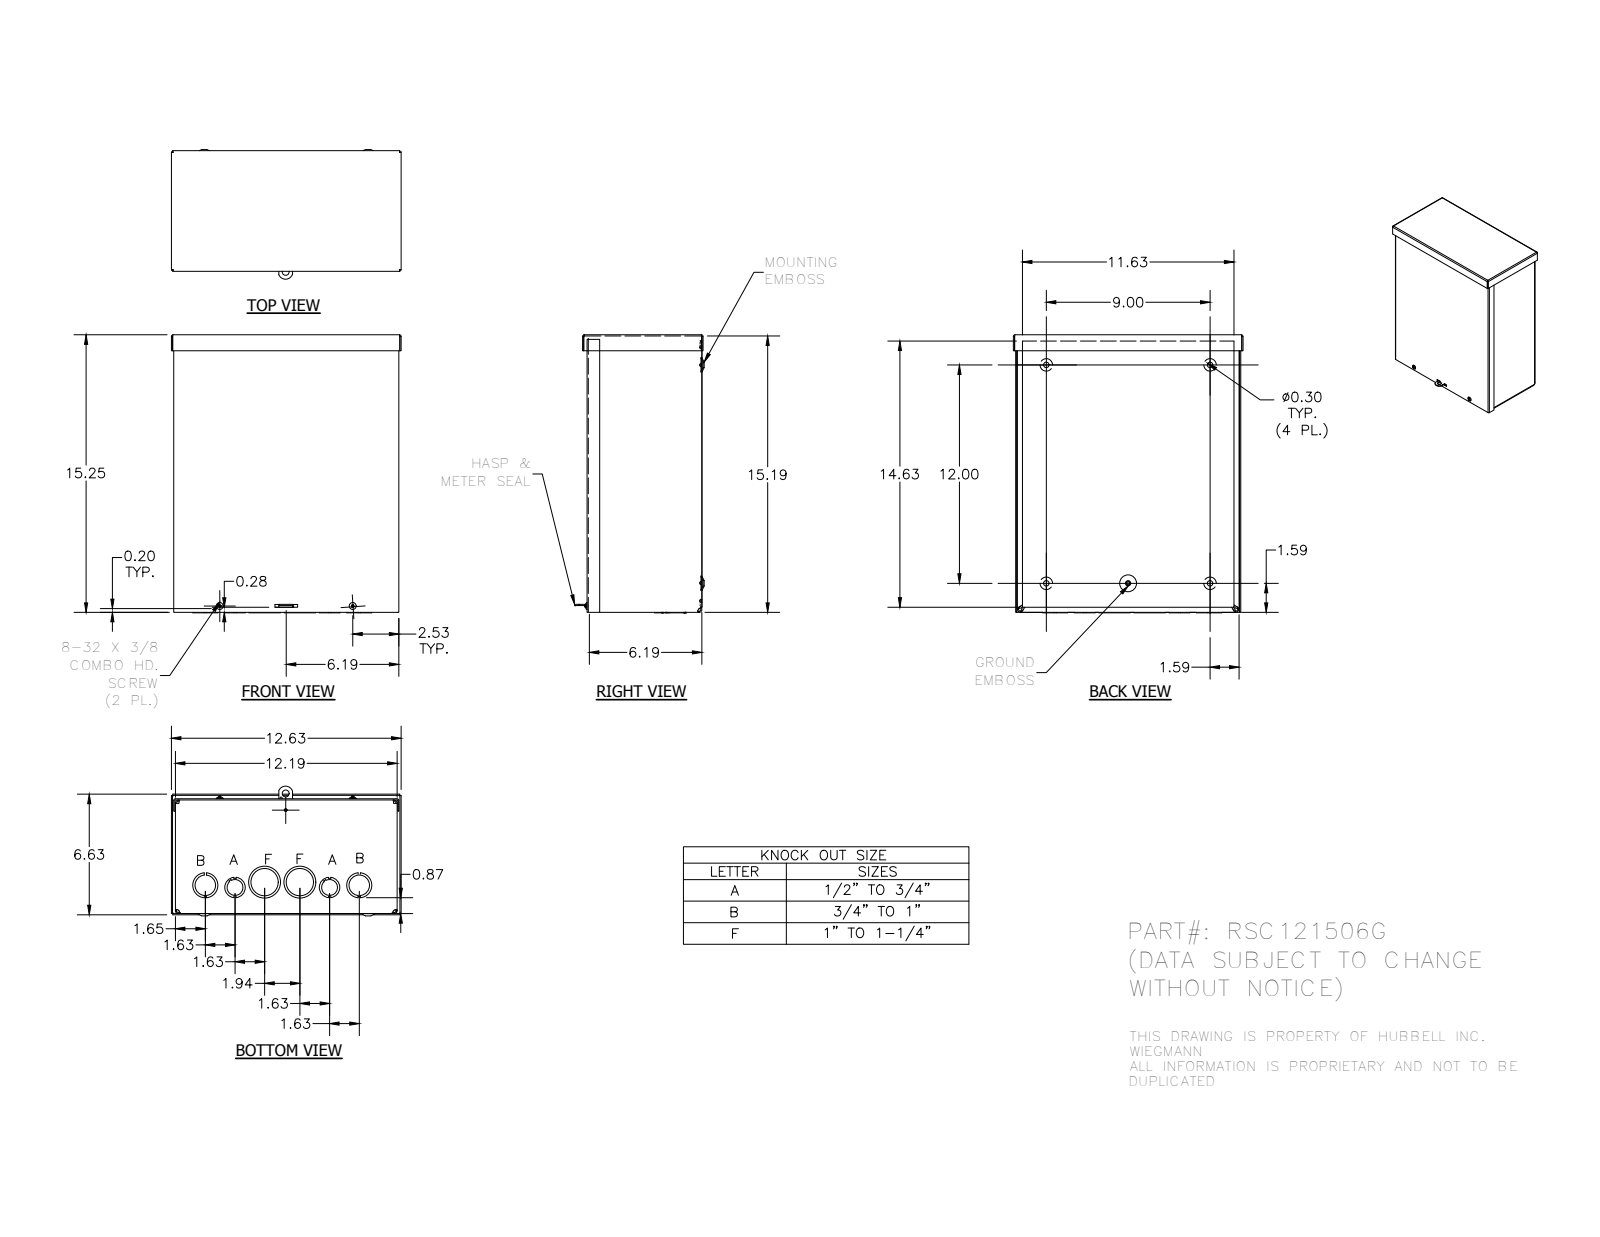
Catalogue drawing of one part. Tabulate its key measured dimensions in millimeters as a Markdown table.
| quantity | value |
| --- | --- |
| part name | RSC121506G_WRAP; RSC1215G_LID; RSC1206G_CAP; 3183 (+4 more) |
| STEP written by | Autodesk Inventor 2014 (AUTOMOTIVE_DESIGN) |
| units | millimeters |
| bodies | 7 solids, 551 faces (264 planar, 143 cylindrical, 144 other) |
| overall size | 388.12 × 320.68 × 180.97 |
| volume | 916 226 mm³ |
| surface area | 1 176 000 mm² |
| round holes (diameter × count) | 7.62 × 4, 7.95 × 4, 28.57 × 4, 3.17 × 2, 3.76 × 2, 22.22 × 2, 34.92 × 2, 38.1 × 2, 44.45 × 2, 3.96 × 1, 4.19 × 1, 9.52 × 1 |
| round bosses / shafts (diameter × count) | 9.75 × 2, 4.17 × 2, 5.8 × 1 |
| partial cylindrical surfaces (radius × count) | 0.25 × 14, 0.79 × 8, 2.37 × 8, 3.17 × 8, 4.75 × 8, 0.79 × 6, 0.63 × 5, 1.4 × 4 |
| main face-to-face distances | 1.58, 1.57, 158.73, 157.15, 307.99, 1.59, 160.32, 158.74, 384.19, 3.15 |
| hole center spacings | 34.43, 41.52, 42.07, 82.91, 90.99, 114.3, 132.15, 173.51 |
